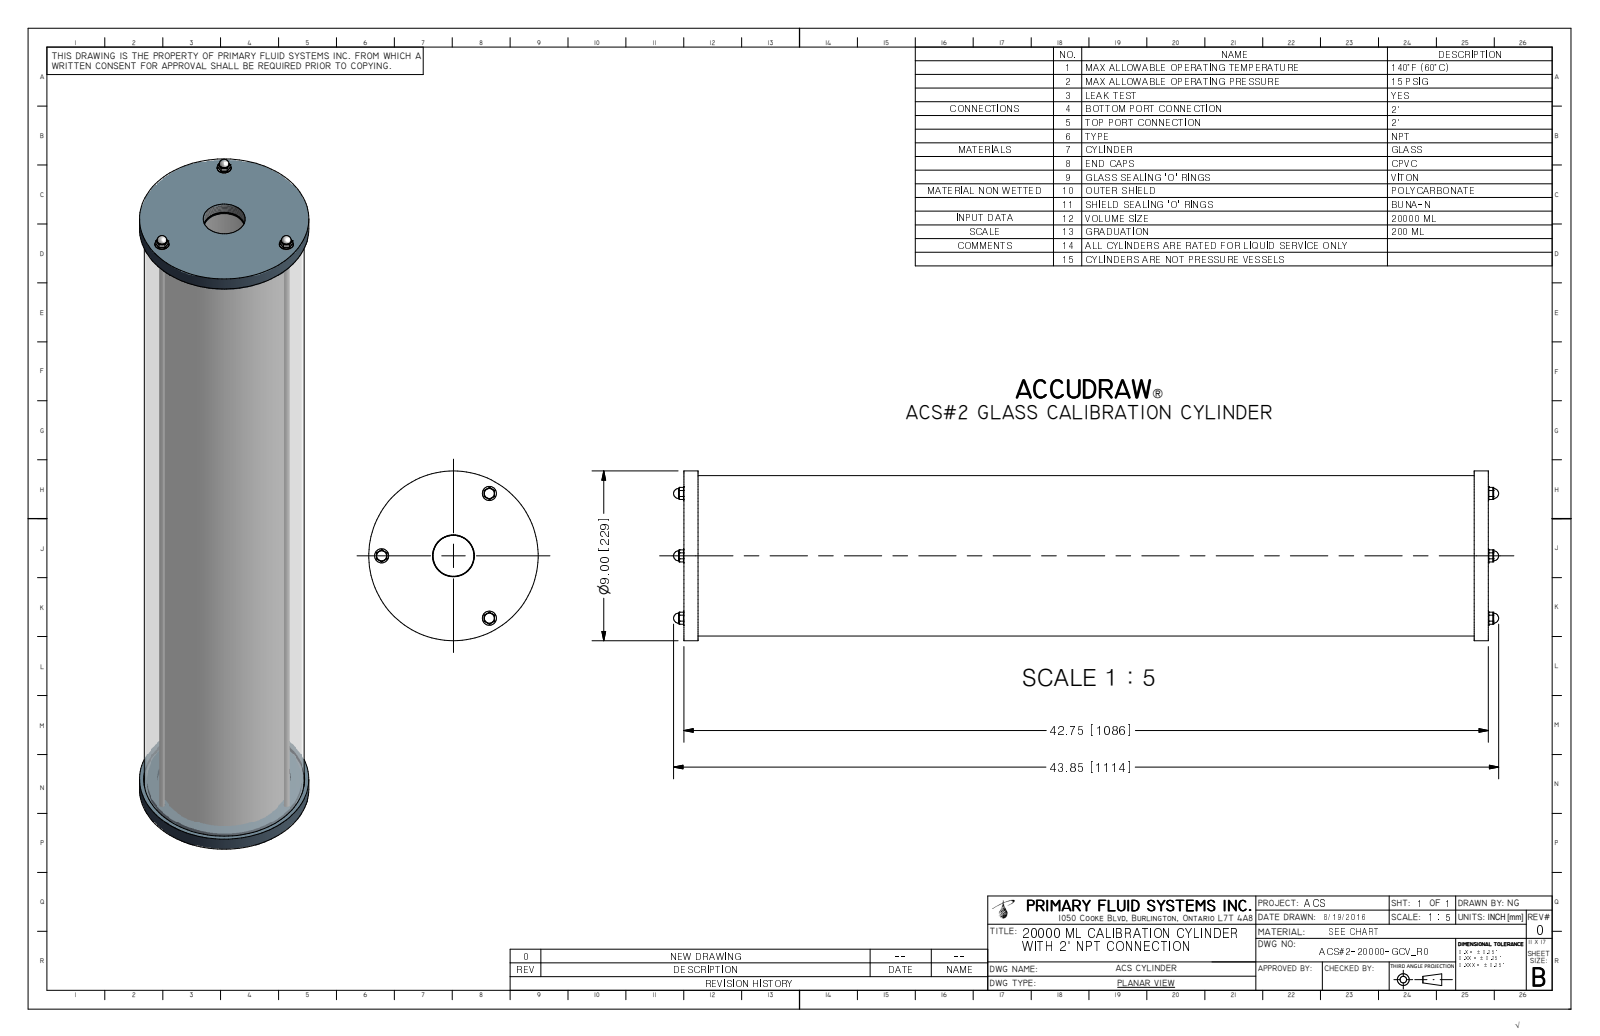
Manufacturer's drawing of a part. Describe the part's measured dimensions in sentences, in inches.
The part is named "ACS#2-20000-GCV_R0; ACS-3-20000-POLY_R3; ACS-2-20000_R6; ACS-1-20000-A_R0 (+3 more)". Its 3-D file was written by "Autodesk Inventor 2009 (AUTOMOTIVE_DESIGN)". It is 19 solids with 219 faces: 80 planar, 113 cylindrical and 26 other. Overall it measures 43.85 by 9 by 9 inches. Its volume is 461.4 cubic inches and its surface area 4 420 square inches. Round holes: 3 of diameter 0.328, 3 of diameter 0.344, 1 of diameter 6.252, 1 of diameter 7.125, 1 of diameter 8.25, 1 of diameter 8.55. Round bosses or shafts: 3 of diameter 0.75, 3 of diameter 0.528, 3 of diameter 0.313, 1 of diameter 9, 1 of diameter 8.5, 1 of diameter 8.2, 1 of diameter 6.804, 1 of diameter 6.165. Partial cylindrical surfaces (rounded edges, fillets, slot ends): 56 of radius 0.005. The main face-to-face distances are 42.75, 0.75, 42, 0.375, 42.375, 0.375, 41.625, 41.25, 42, 0.475. The hole center spacings are 3.817, 6.611, 6.611.
